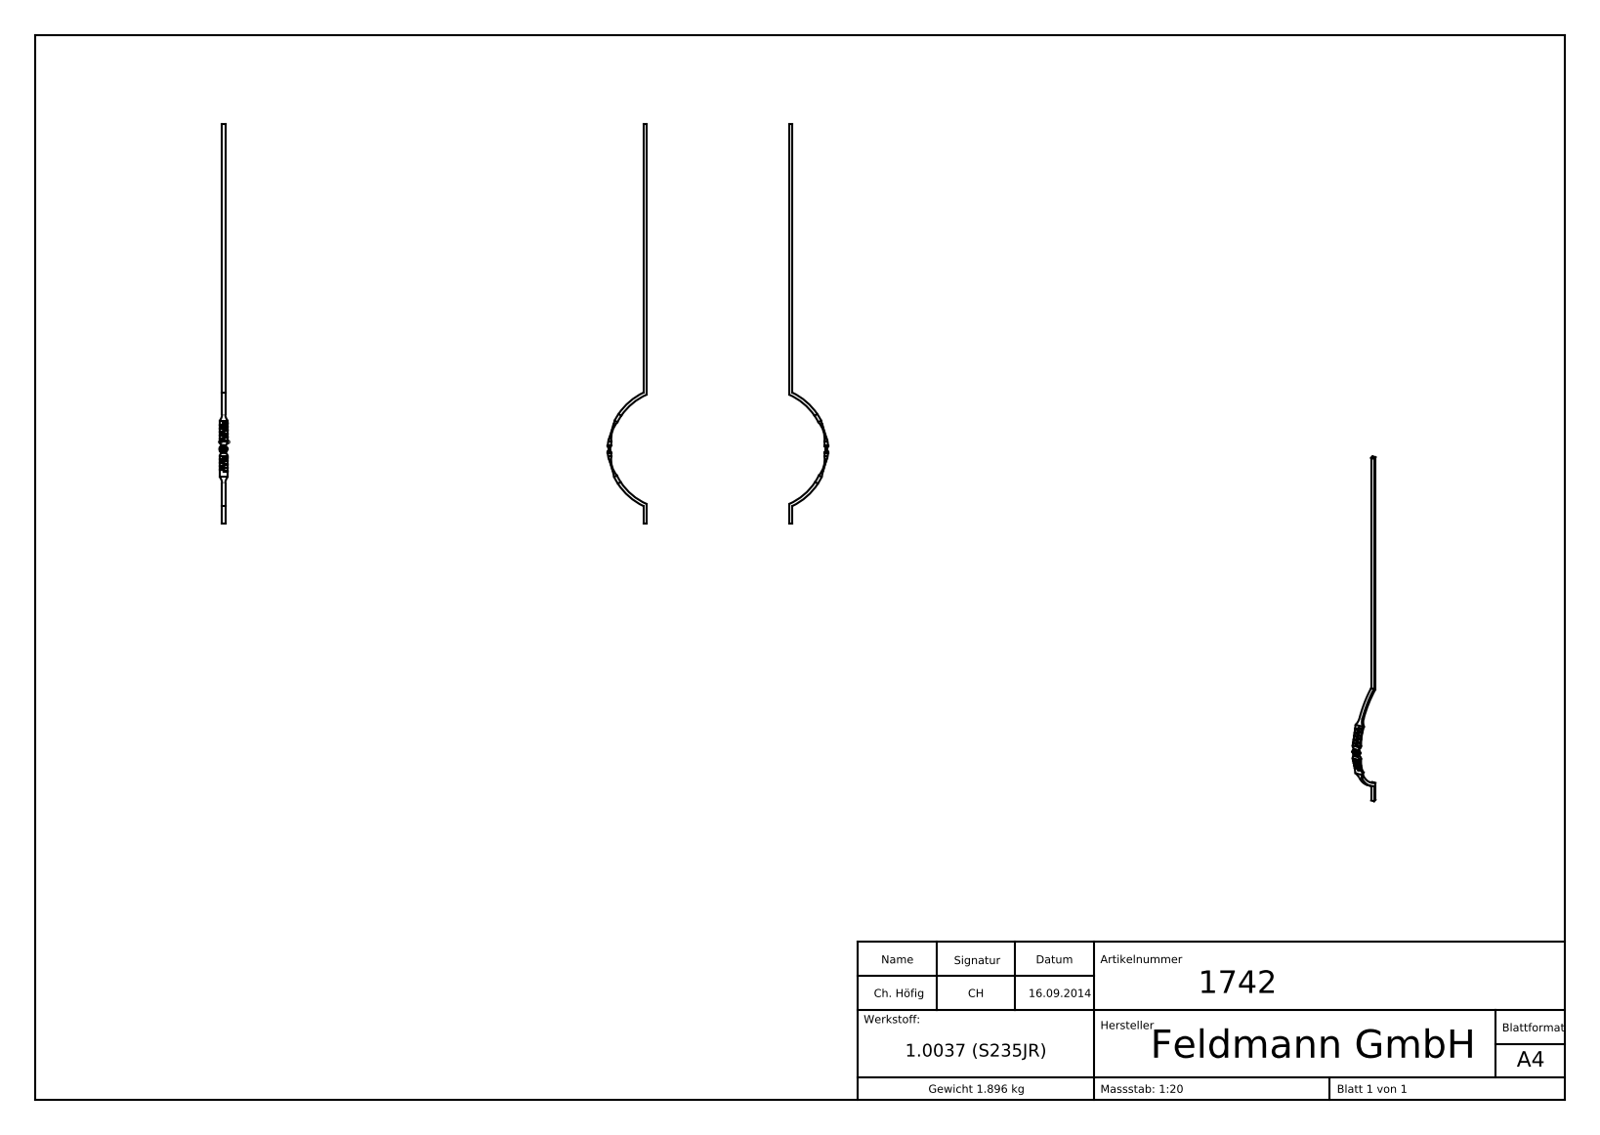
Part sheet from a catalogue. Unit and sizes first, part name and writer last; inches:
Units: inches
Overall size (bounding box): 59.055 × 5.75 × 1.23
Round bosses / shafts (diameter × count): ⌀1.181 ×1
Partial cylindrical surfaces — rounded edges, fillets, slot ends (radius × count): R0.079 ×40, R0.059 ×4, R0.591 ×4, R1.969 ×4, R23.58 ×3, R0.866 ×2, R3.513 ×1, R3.633 ×1
Main face-to-face distances: 0.472, 0.354, 0.827, 1.181, 59.055, 5.276, 5.748, 0.039, 11.004, 48.051
Volume: 14.83 in³ · Surface area: 130.2 in²
Bodies: 1 solid, 340 faces (128 planar, 102 cylindrical, 110 other)
Part name (STEP PRODUCT): 1742
STEP written by: SolidWorks 2015 (CONFIG_CONTROL_DESIGN)
